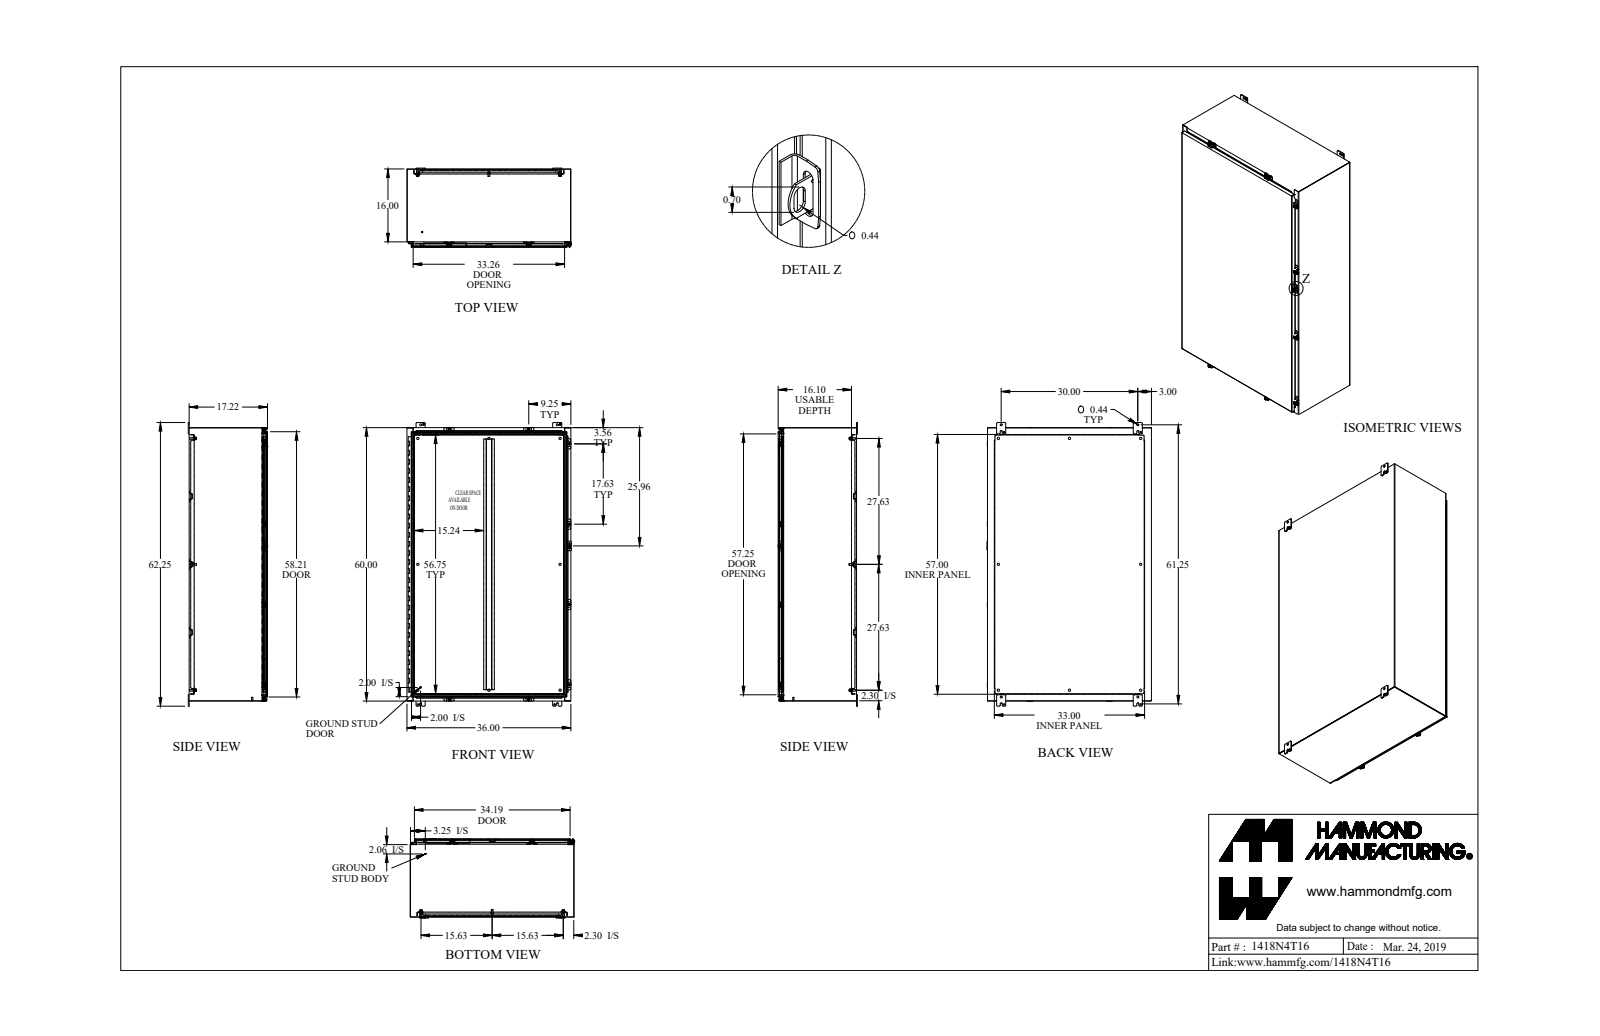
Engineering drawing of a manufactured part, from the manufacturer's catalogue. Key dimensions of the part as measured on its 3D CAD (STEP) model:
Part name (STEP PRODUCT): 1418N4T16_Default
STEP written by: SolidWorks 2019 (CONFIG_CONTROL_DESIGN)
Units: inches
Bodies: 69 solids, 2458 faces (1445 planar, 913 cylindrical, 100 other)
Overall size (bounding box): 62.25 × 36.126 × 17.437
Volume: 819.8 in³ · Surface area: 21 500 in²
Round holes (diameter × count): ⌀0.213 ×8, ⌀0.265 ×8, ⌀0.375 ×8, ⌀0.5 ×8, ⌀0.307 ×4, ⌀0.313 ×4, ⌀0.437 ×4, ⌀0.445 ×4, ⌀0.125 ×1, ⌀0.187 ×1
Round bosses / shafts (diameter × count): ⌀0.65 ×8, ⌀0.5 ×8, ⌀0.39 ×8, ⌀0.375 ×8, ⌀0.33 ×8, ⌀0.244 ×8, ⌀1 ×4, ⌀0.281 ×2
Partial cylindrical surfaces — rounded edges, fillets, slot ends (radius × count): R0.25 ×44, R0.048 ×39, R0.143 ×39, R0.188 ×36, R0.036 ×22, R0.108 ×22, R0.116 ×16, R0.141 ×16
Main face-to-face distances: 0.072, 17.143, 17.071, 17.215, 0.095, 35.928, 16.111, 16.039, 1.032, 1.104
Hole centre spacings: 7.196, 15.625, 24.468, 55.25, 57.417, 27.625, 31.25, 57.785
